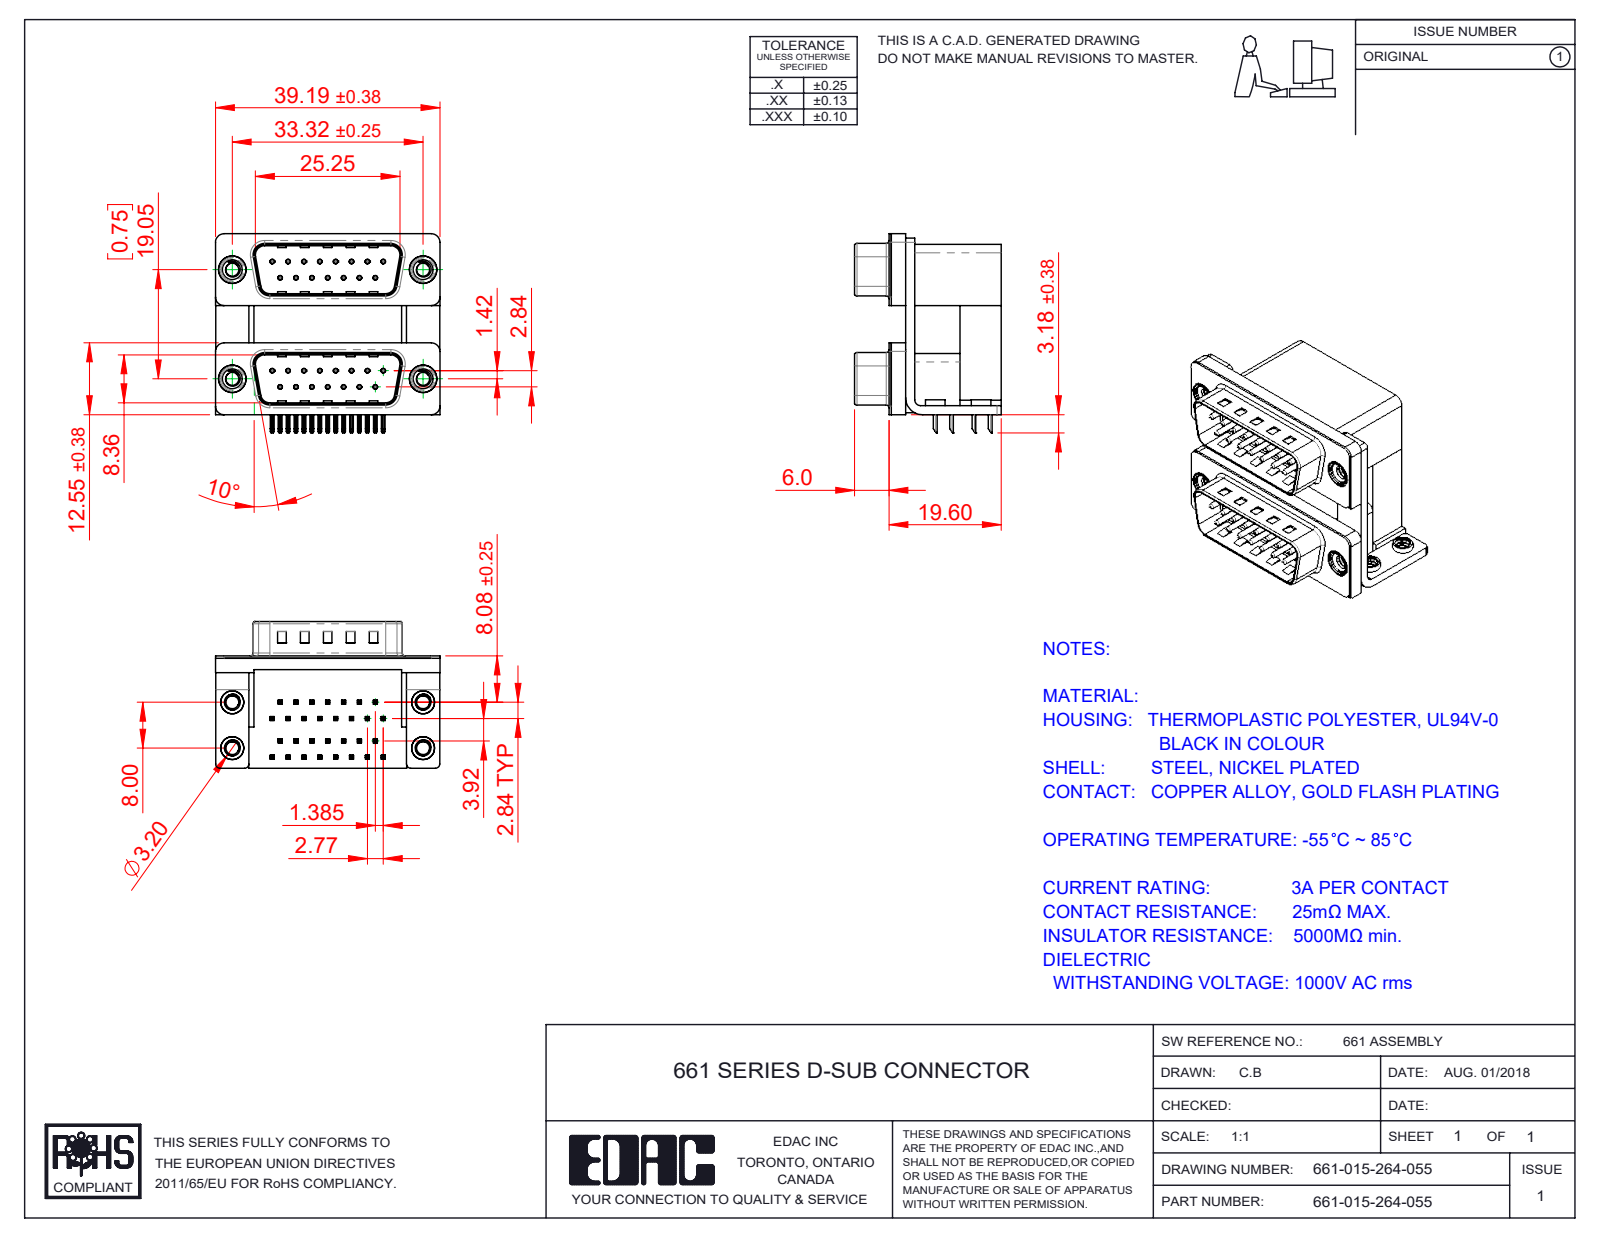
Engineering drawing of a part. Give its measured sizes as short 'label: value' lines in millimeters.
name: 661 Contact Top Lower; 661 Mounting Bracket_ThruM; 661 Shell_15 Contacts; 661 Housing Lower_15 Contacts (+8 more)
written by: SolidWorks 2020 (CONFIG_CONTROL_DESIGN)
unit: mm
bodies: 45 solids, 3102 faces (1846 planar, 930 cylindrical, 326 other)
size: 39.19 × 34.78 × 25.6
volume: 14 428 mm³; area: 15 914 mm²
holes: 30× ⌀0.35, 30× ⌀0.8, 8× ⌀2.26, 4× ⌀2.75, 4× ⌀3.2, 4× ⌀3.5, 4× ⌀4, 4× ⌀4.8, 4× ⌀5
bosses: 30× ⌀0.75, 4× ⌀4.9, 4× ⌀4.75, 4× ⌀4, 4× ⌀3.9, 4× ⌀3.4
rounds: 120× R0.25, 60× R0.12, 16× R0.5, 16× R1.5, 8× R0.75, 8× R0.9, 8× R1.6, 8× R2
face distances: 0.4, 19.05, 19.2, 10.69, 16.7, 2.5, 7.2, 12, 9.5, 18.7
hole spacings: 3.16, 2.77, 19.25, 5.54, 19.84, 8.31, 20.78, 19.05
